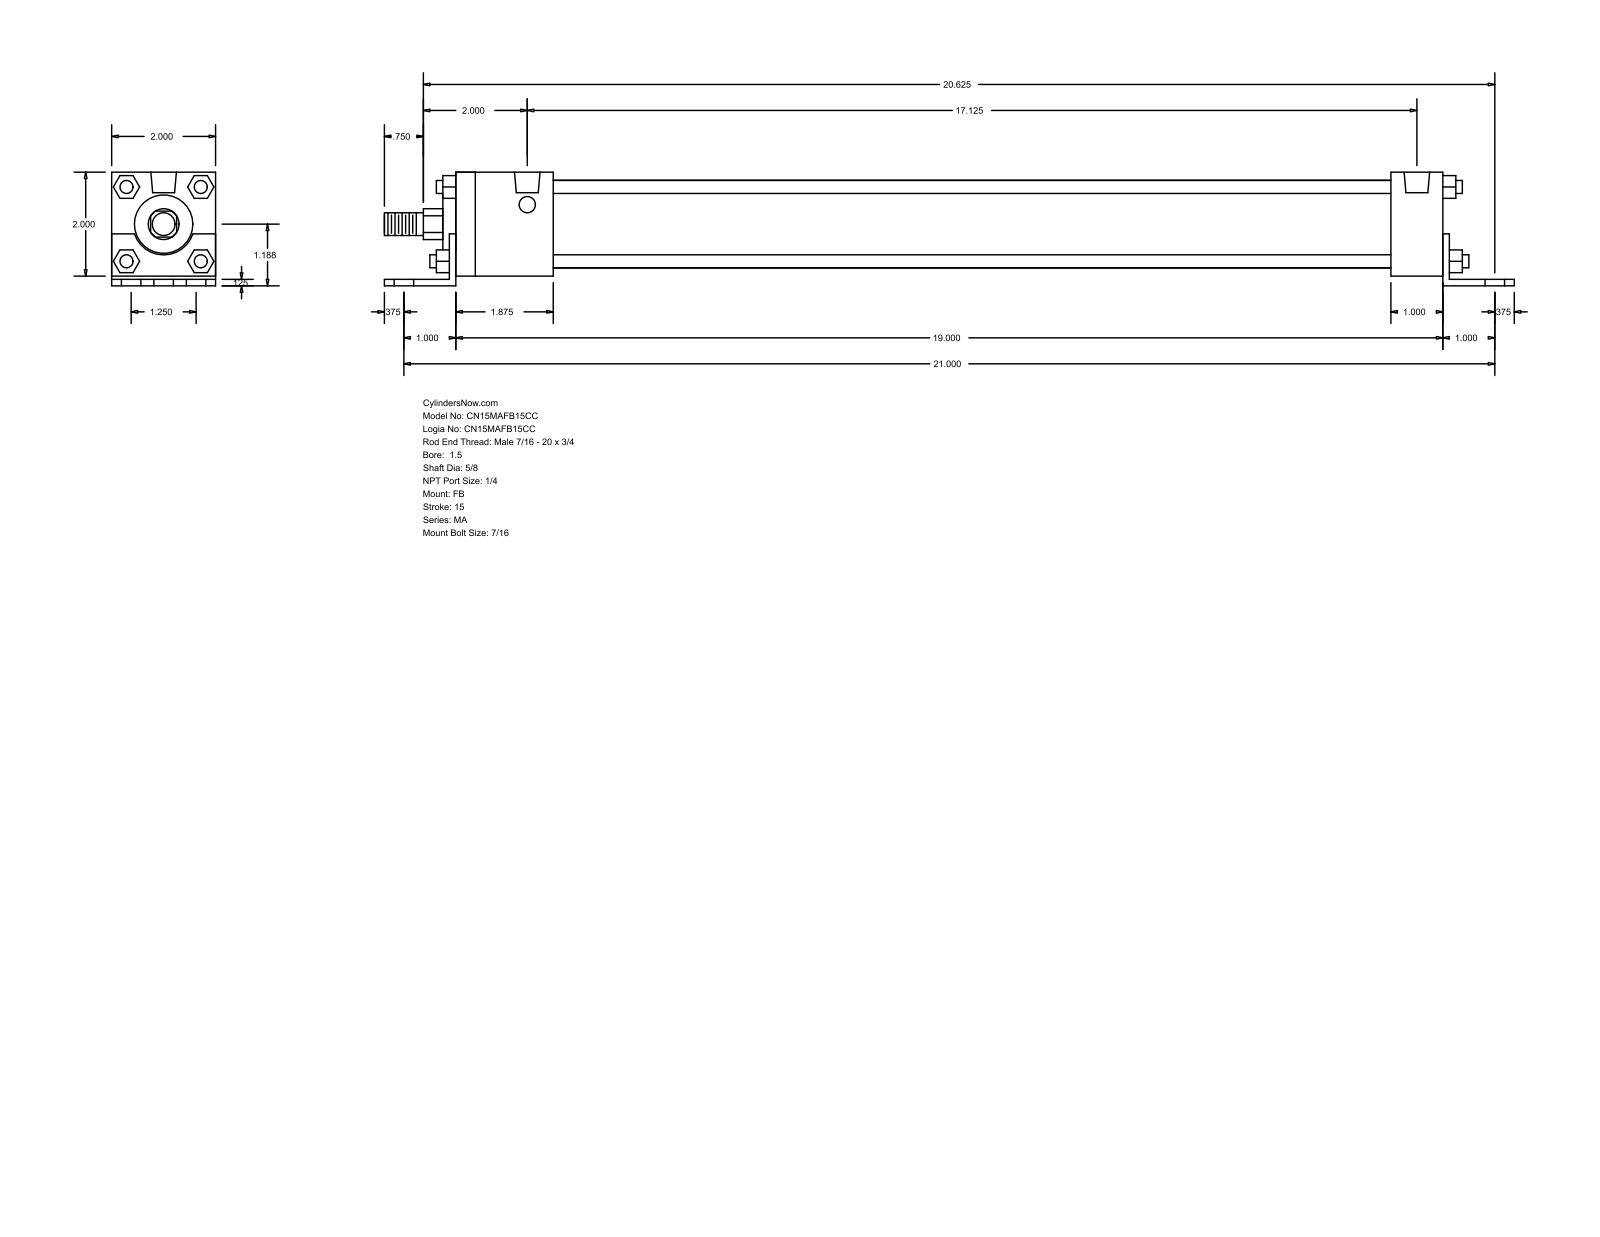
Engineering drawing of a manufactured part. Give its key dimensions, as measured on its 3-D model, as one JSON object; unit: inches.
{"part_name": "MA_FB__0150_0.625", "step_written_by": "GSSL Pune (CONFIG_CONTROL_DESIGN)", "units": "inches", "bodies": {"solids": 0, "faces": 140, "planar": 105, "cylindrical": 35, "other": 0}, "overall_size": [21.75, 2.187, 2], "round_holes": [[0.437, 6], [0.313, 4], [0.492, 2]], "round_bosses_or_shafts": [[0.25, 4], [1.69, 1], [1.125, 1], [0.625, 1], [0.437, 1]], "partial_cylinders_radius": [[0.297, 1], [0.593, 1]], "face_to_face_distances": [2, 0.125, 0.187, 2.187, 0.063, 2.063, 1.125, 19.25, 0.125, 19.375], "hole_center_spacings": [0.625, 21.01, 21, 1.25, 1.626, 2.456, 17.125, 18.636]}
